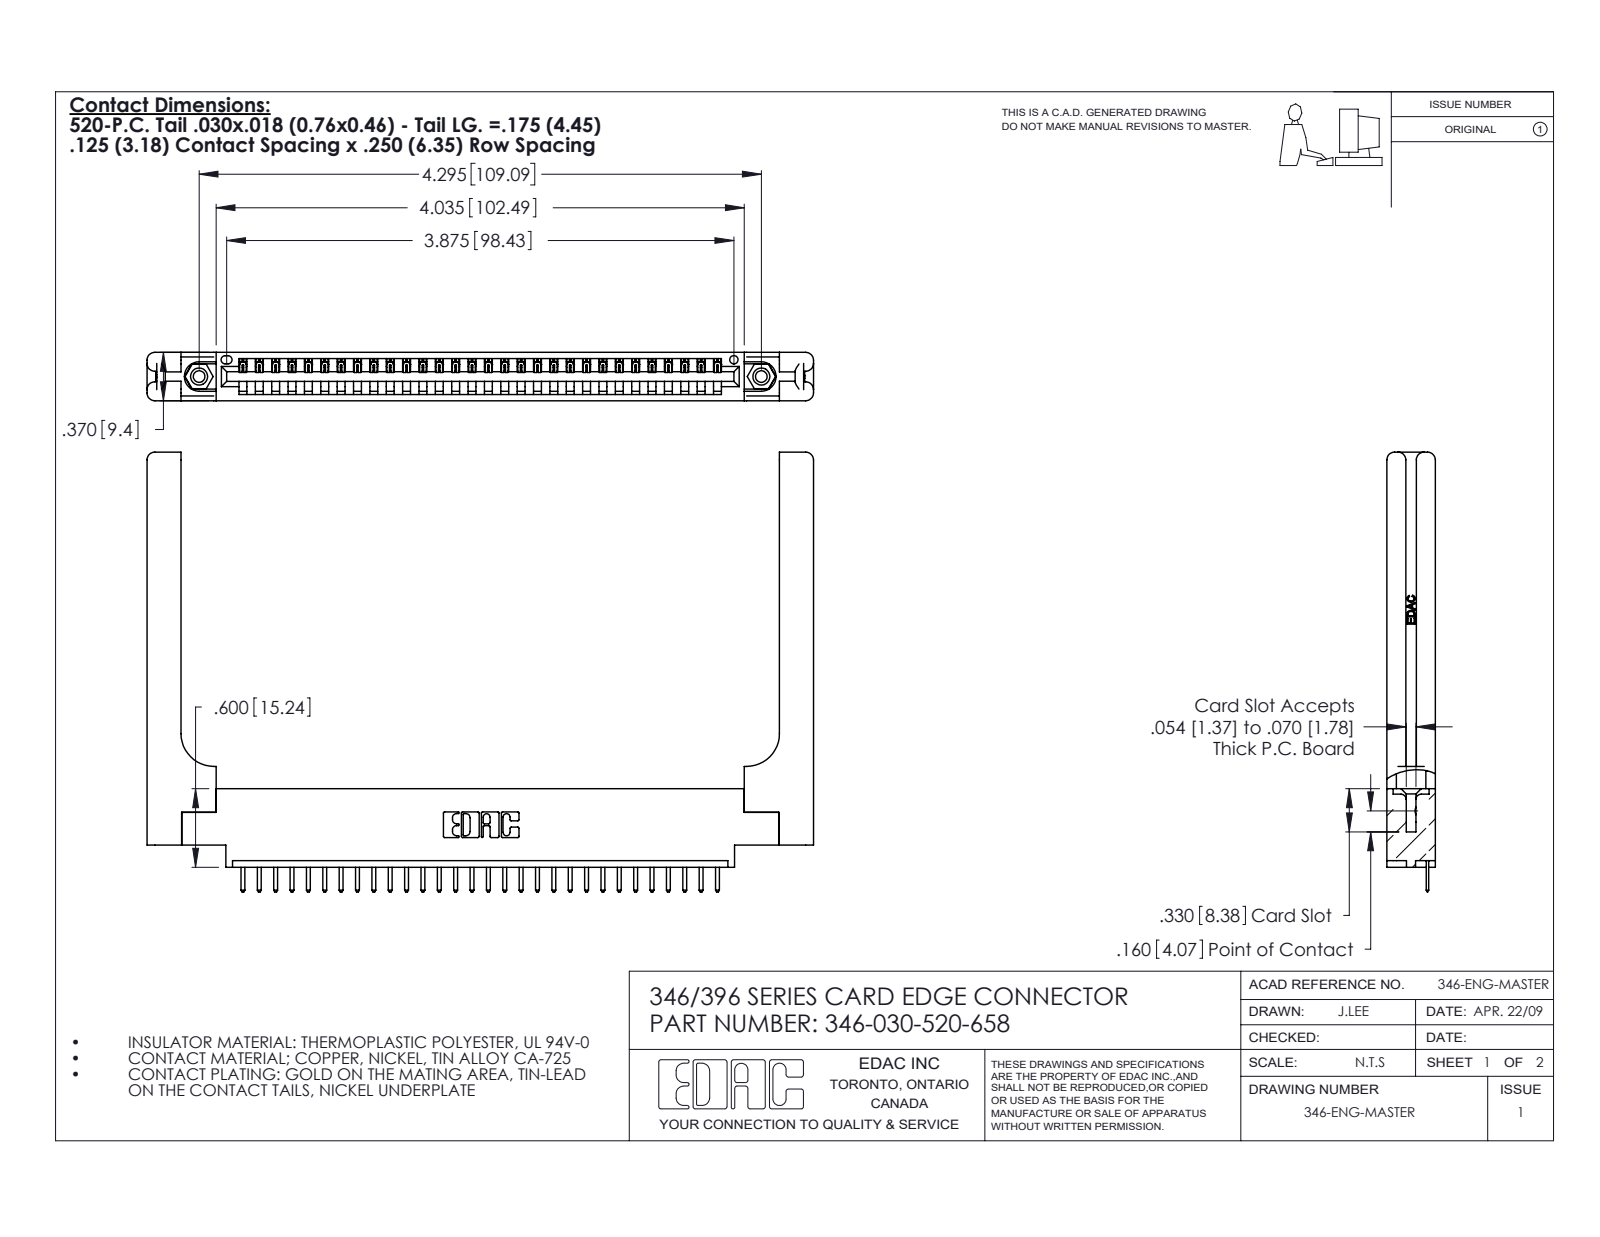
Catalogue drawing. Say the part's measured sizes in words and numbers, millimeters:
The part is named "345-250-001_345-250-001-102; 346-030-520-658; 345-292-001_345-293-120; 346 Part_0.170 Offset - 0.156 Dia-TH (+1 more)". Its 3-D file was written by "SolidWorks 2020 (CONFIG_CONTROL_DESIGN)". It is 35 solids with 2256 faces: 1502 planar, 694 cylindrical and 60 other. Overall it measures 129.3 by 85.3 by 9.4 millimeters. Its volume is 19 550 cubic millimeters and its surface area 19 990 square millimeters. Round holes: 2 of diameter 2.3, 2 of diameter 3.2, 2 of diameter 4, 1 of diameter 1.6. Round bosses or shafts: 2 of diameter 3.9. Partial cylindrical surfaces (rounded edges, fillets, slot ends): 62 of radius 0.3, 60 of radius 0.2, 22 of radius 0.3, 16 of radius 1.5, 6 of radius 0.2, 6 of radius 0.8, 3 of radius 0.7, 2 of radius 0.8. The main face-to-face distances are 9.4, 1.8, 1.2, 8.2, 3.8, 3.8, 6.4, 7.6, 0.6, 5.6. The hole center spacings are 6.2, 103.8, 109.1.
